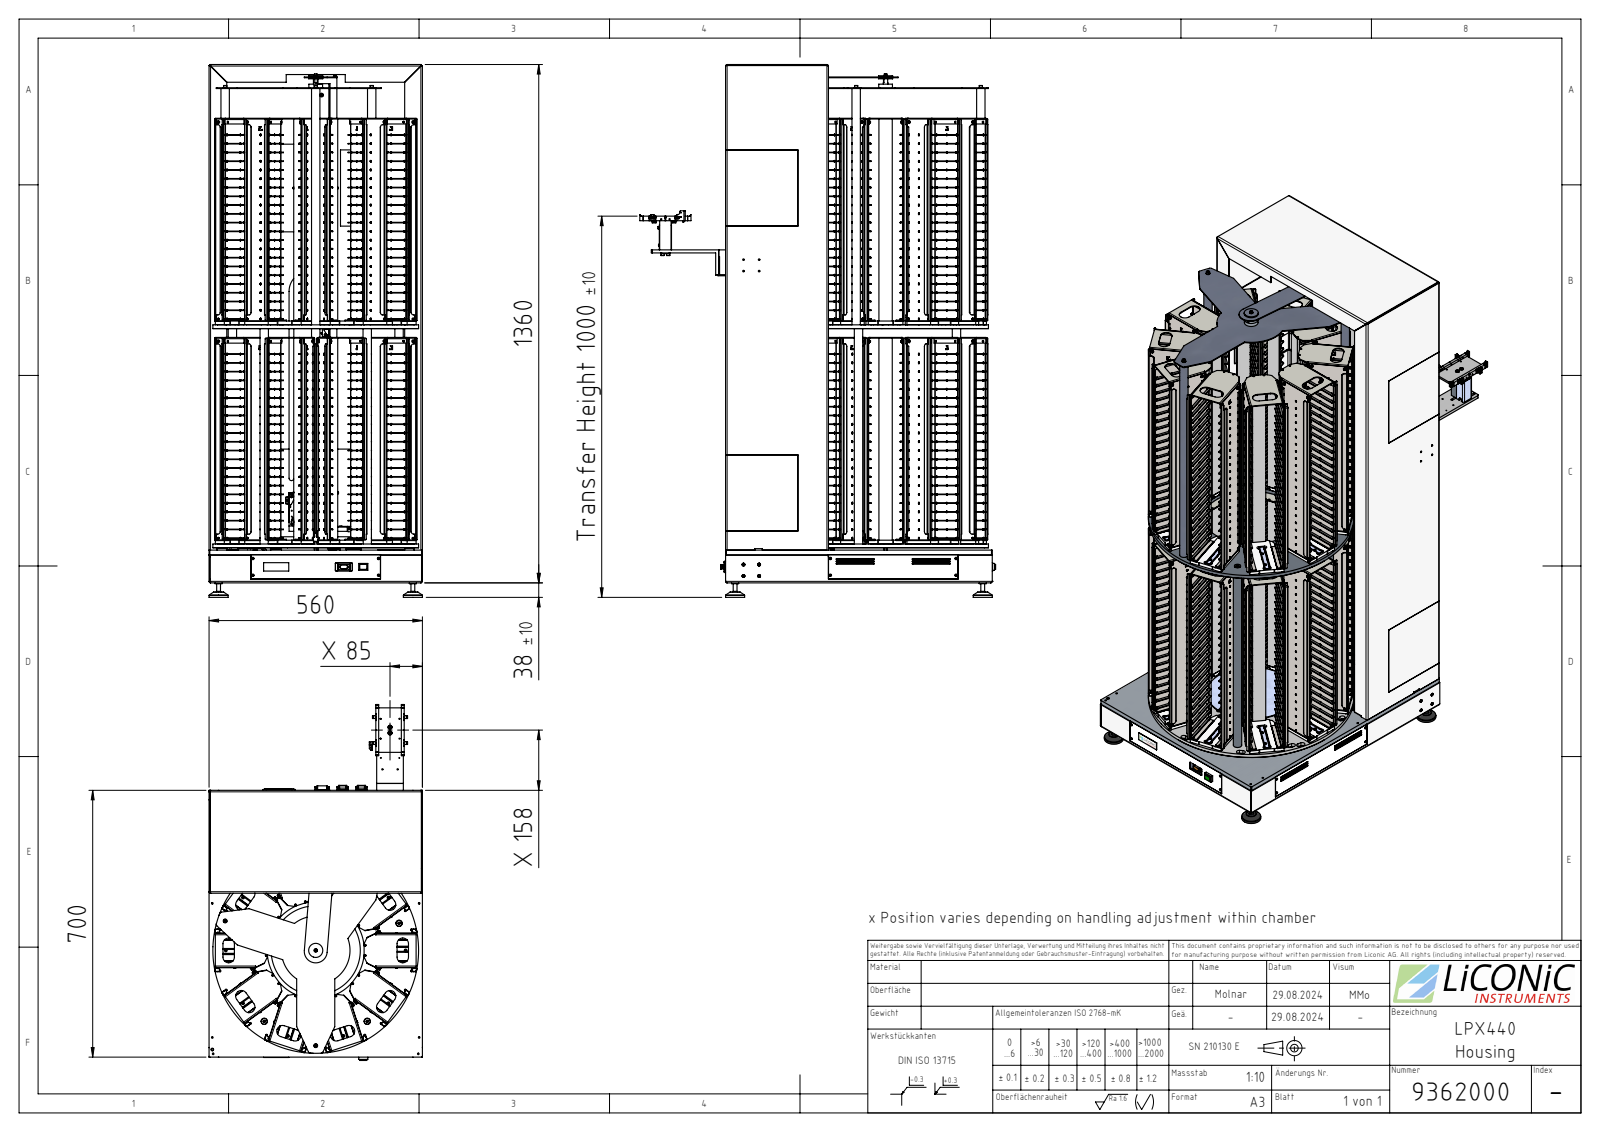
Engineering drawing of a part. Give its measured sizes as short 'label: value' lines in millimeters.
name: 9362000
written by: SolidWorks 2022 (AUTOMOTIVE_DESIGN)
unit: mm
bodies: 58 solids, 8430 faces (4526 planar, 3748 cylindrical, 156 other)
size: 1398 × 933.98 × 560.01
volume: 16 630 000 mm³; area: 8 042 000 mm²
holes: 88× ⌀4, 74× ⌀4.2, 59× ⌀2.5, 47× ⌀3.3, 28× ⌀6.5, 16× ⌀7.1, 10× ⌀3.4, 10× ⌀6.2, 8× ⌀3.1, 8× ⌀4.7, 8× ⌀6.8, 8× ⌀8
bosses: 8× ⌀22, 4× ⌀50.01, 4× ⌀10, 3× ⌀1.5, 1× ⌀540, 1× ⌀234, 1× ⌀15.5, 1× ⌀14.5
rounds: 832× R0.1, 832× R0.25, 467× R2, 127× R5, 114× R2.5, 60× R1, 36× R1.5, 36× R3
face distances: 2, 558, 10, 560, 72, 556, 74, 575, 12, 86
hole spacings: 23, 46, 69, 92, 115, 138, 161, 184
